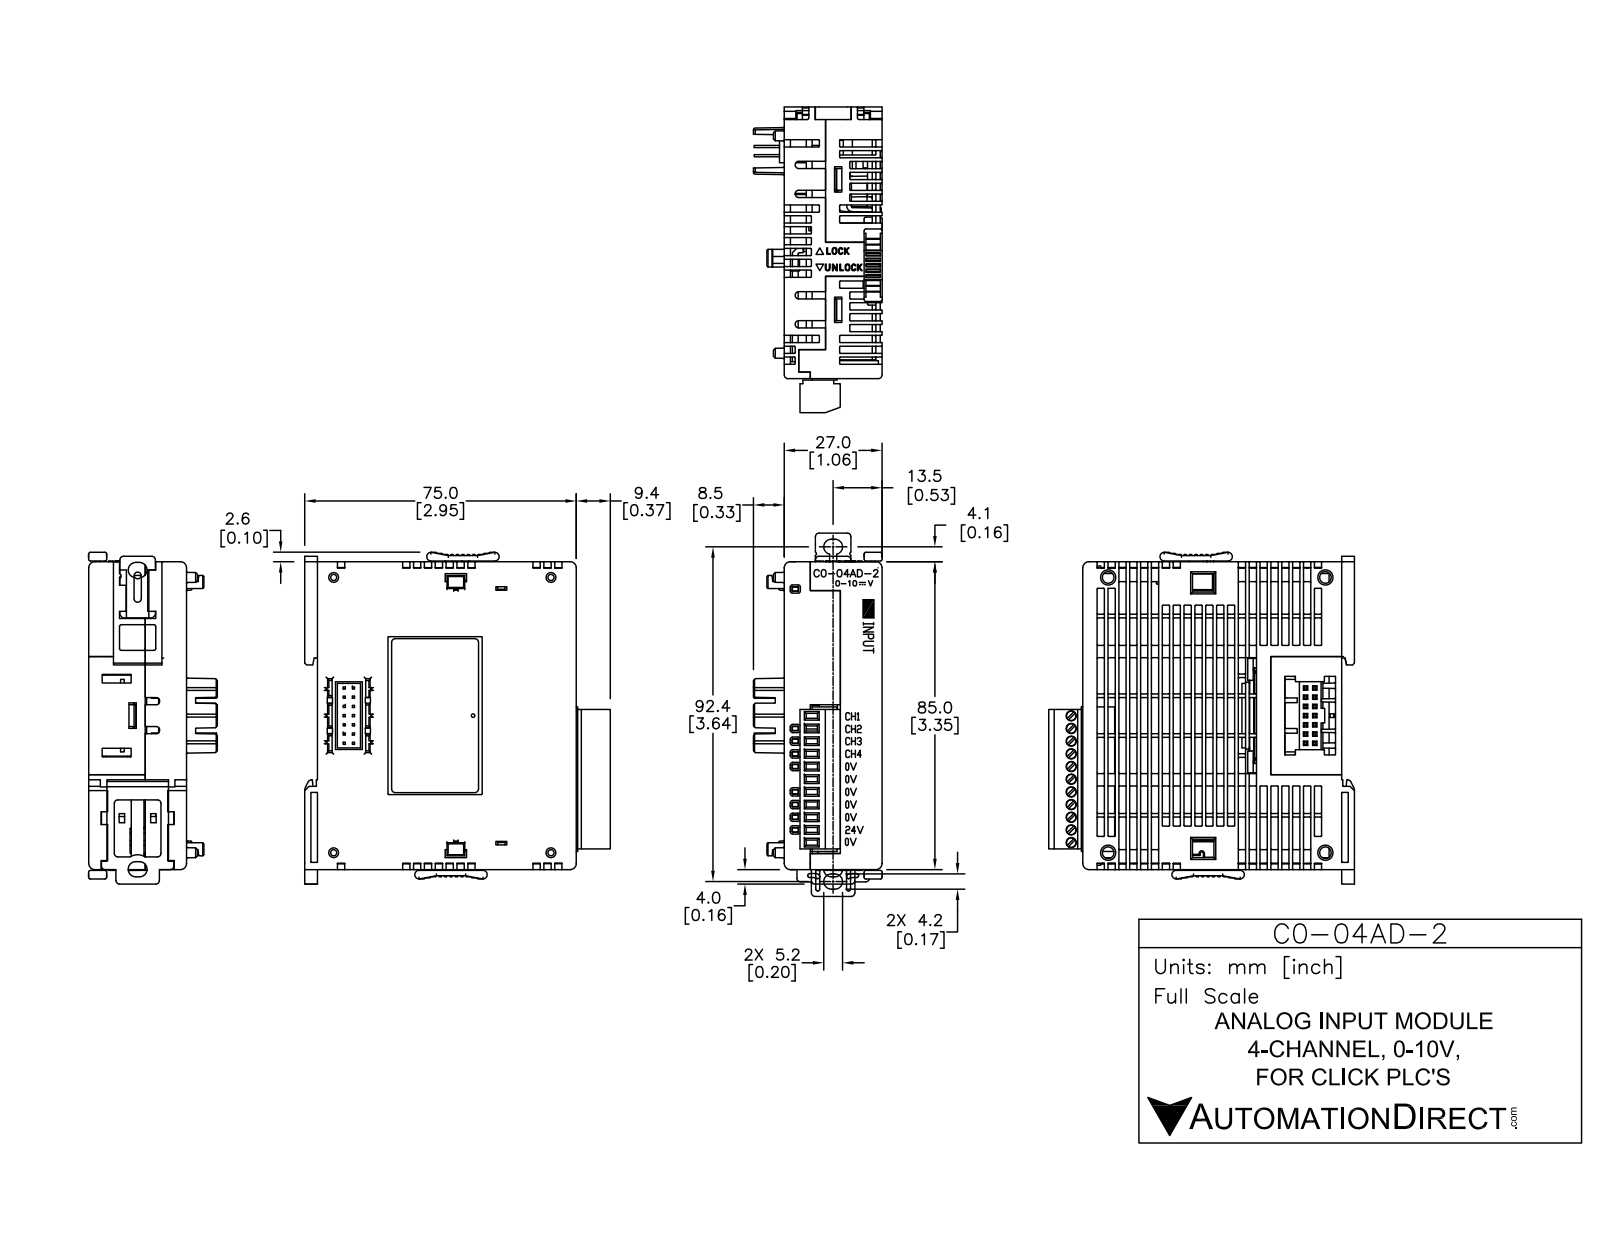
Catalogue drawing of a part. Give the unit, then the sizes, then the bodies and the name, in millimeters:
Units: millimetres
Overall size (bounding box): 91.6 × 84.4 × 35.55
Round holes (diameter × count): ⌀1 ×11, ⌀2.8 ×11, ⌀3.2 ×4, ⌀2 ×2
Round bosses / shafts (diameter × count): ⌀2.6 ×11, ⌀1.9 ×1
Partial cylindrical surfaces — rounded edges, fillets, slot ends (radius × count): R0.2 ×570, R0.5 ×43, R0.3 ×22, R1 ×18, R1.2 ×12, R2.8 ×11, R1.7 ×6, R2.1 ×4
Main face-to-face distances: 27.01, 0.5, 0.51, 26.5, 71.5, 1.7, 85, 26.3, 26.81, 84.5
Hole centre spacings: 3.5, 7, 10.5, 14, 17.5, 21, 24.5, 28
Volume: 162 508 mm³ · Surface area: 31 791 mm²
Bodies: 1 solid, 3792 faces (2700 planar, 968 cylindrical, 124 other)
Part name (STEP PRODUCT): C0-04AD-2
STEP written by: SolidWorks 2013 (AUTOMOTIVE_DESIGN)
